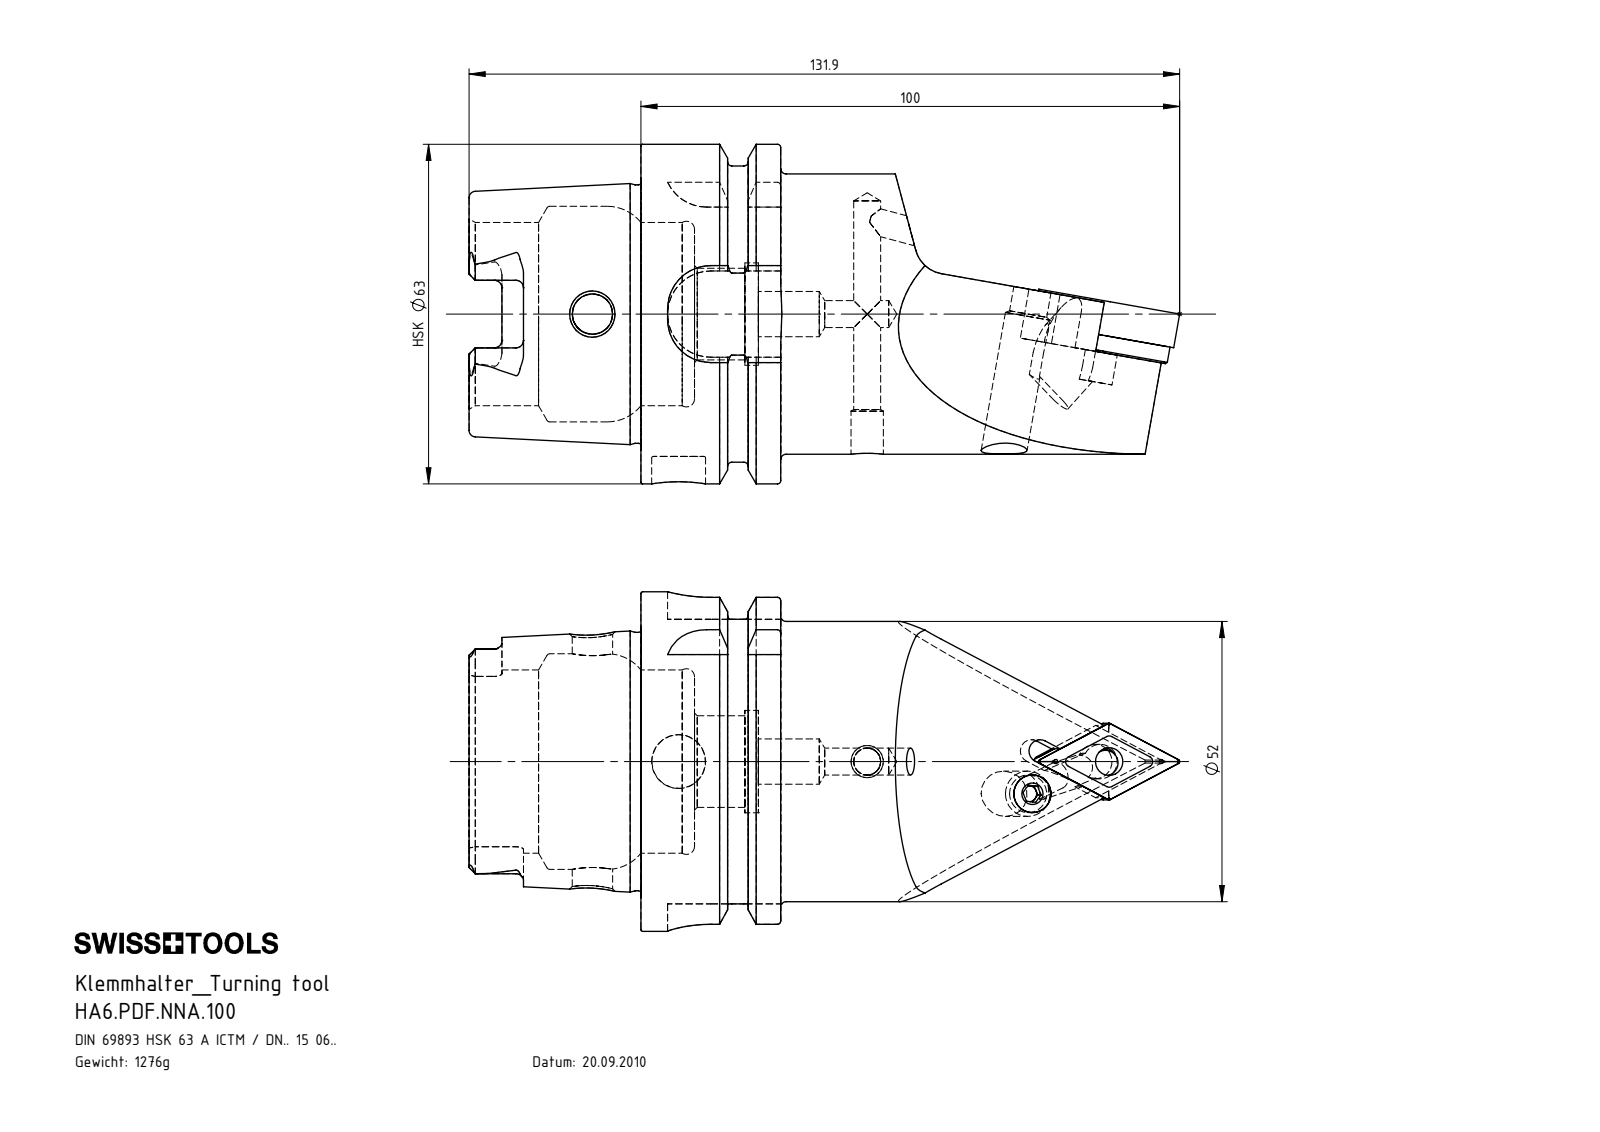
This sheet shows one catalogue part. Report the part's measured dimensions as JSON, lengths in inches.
{"part_name": "HA6.PDF.NNA.100; WDF-ER2.101.003_A; WCD-ER1.101.000; WCD-ER4.101.017_A (+4 more)", "step_written_by": "SolidWorks 2012 (AUTOMOTIVE_DESIGN)", "units": "inches", "bodies": {"solids": 8, "faces": 370, "planar": 117, "cylindrical": 102, "other": 151}, "overall_size": [5.193, 2.48, 2.48], "volume_in3": 9.977, "surface_area_in2": 53.78, "round_holes": [[0.197, 3], [0.331, 2], [0.203, 1], [0.252, 1], [0.276, 1], [0.295, 1], [0.394, 1], [0.669, 1], [0.748, 1], [1.339, 1], [1.575, 1]], "round_bosses_or_shafts": [[2.48, 1], [2.163, 1], [2.047, 1], [1.887, 1], [0.315, 1], [0.311, 1], [0.252, 1], [0.236, 1]], "partial_cylinders_radius": [[0.055, 6], [0.016, 4], [0.039, 4], [0.315, 4], [0.098, 2], [0.111, 2], [0.113, 2], [0.126, 2]], "face_to_face_distances": [1.022, 0.63, 0.392, 0.468, 1.256, 1.648, 2.278, 0.238, 2.079, 0.858], "hole_center_spacings": [0.615, 1.378]}
